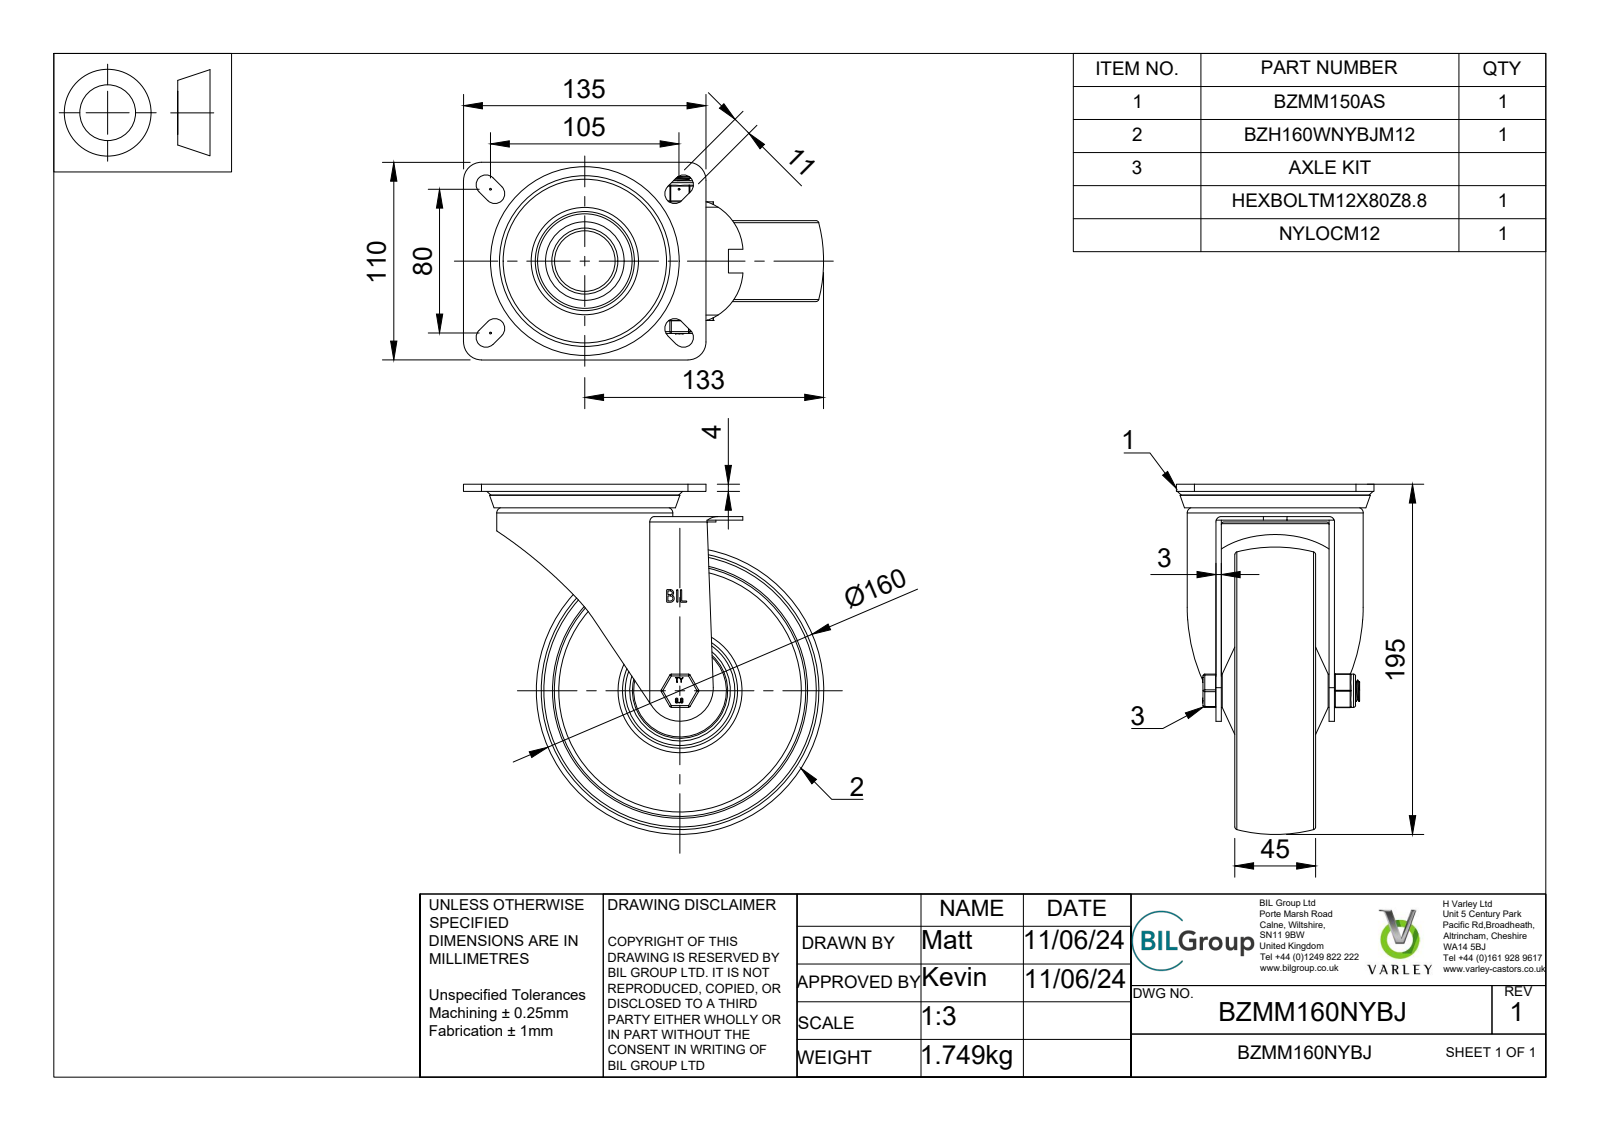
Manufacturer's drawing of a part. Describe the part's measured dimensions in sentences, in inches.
The part is named "BZMM160NYBJ v4; BZH160WNYBJM12 v1; NYLON WHEEL; NYLON WHEEL2 (+7 more)". Its 3-D file was written by "Autodesk Translation Framework v13.14.0.145 (AUTOMOTIVE_DESIGN)". It is 62 solids with 791 faces: 283 planar, 177 cylindrical and 331 other. Overall it measures 7.894 by 7.677 by 4.331 inches. Its volume is 31.66 cubic inches and its surface area 368.1 square inches. Round holes: 1 of diameter 0.472, 1 of diameter 0.48, 1 of diameter 0.488, 1 of diameter 0.551, 1 of diameter 1.122, 1 of diameter 1.213, 1 of diameter 1.329, 1 of diameter 1.398, 1 of diameter 1.565, 1 of diameter 1.587, 1 of diameter 1.594, 1 of diameter 1.654. Round bosses or shafts: 1 of diameter 3.858, 1 of diameter 3.071, 1 of diameter 2.52, 1 of diameter 2.087, 1 of diameter 1.969, 1 of diameter 1.89, 1 of diameter 1.606, 1 of diameter 1.232. Partial cylindrical surfaces (rounded edges, fillets, slot ends): 18 of radius 0.02, 12 of radius 0.039, 8 of radius 0.217, 4 of radius 0.059, 4 of radius 0.394, 2 of radius 0.118, 2 of radius 1.18, 1 of radius 0.65. The main face-to-face distances are 0.118, 0.354, 0.197, 0.157, 0.128, 0.63, 0.512, 1.24, 2.48, 0.472.
